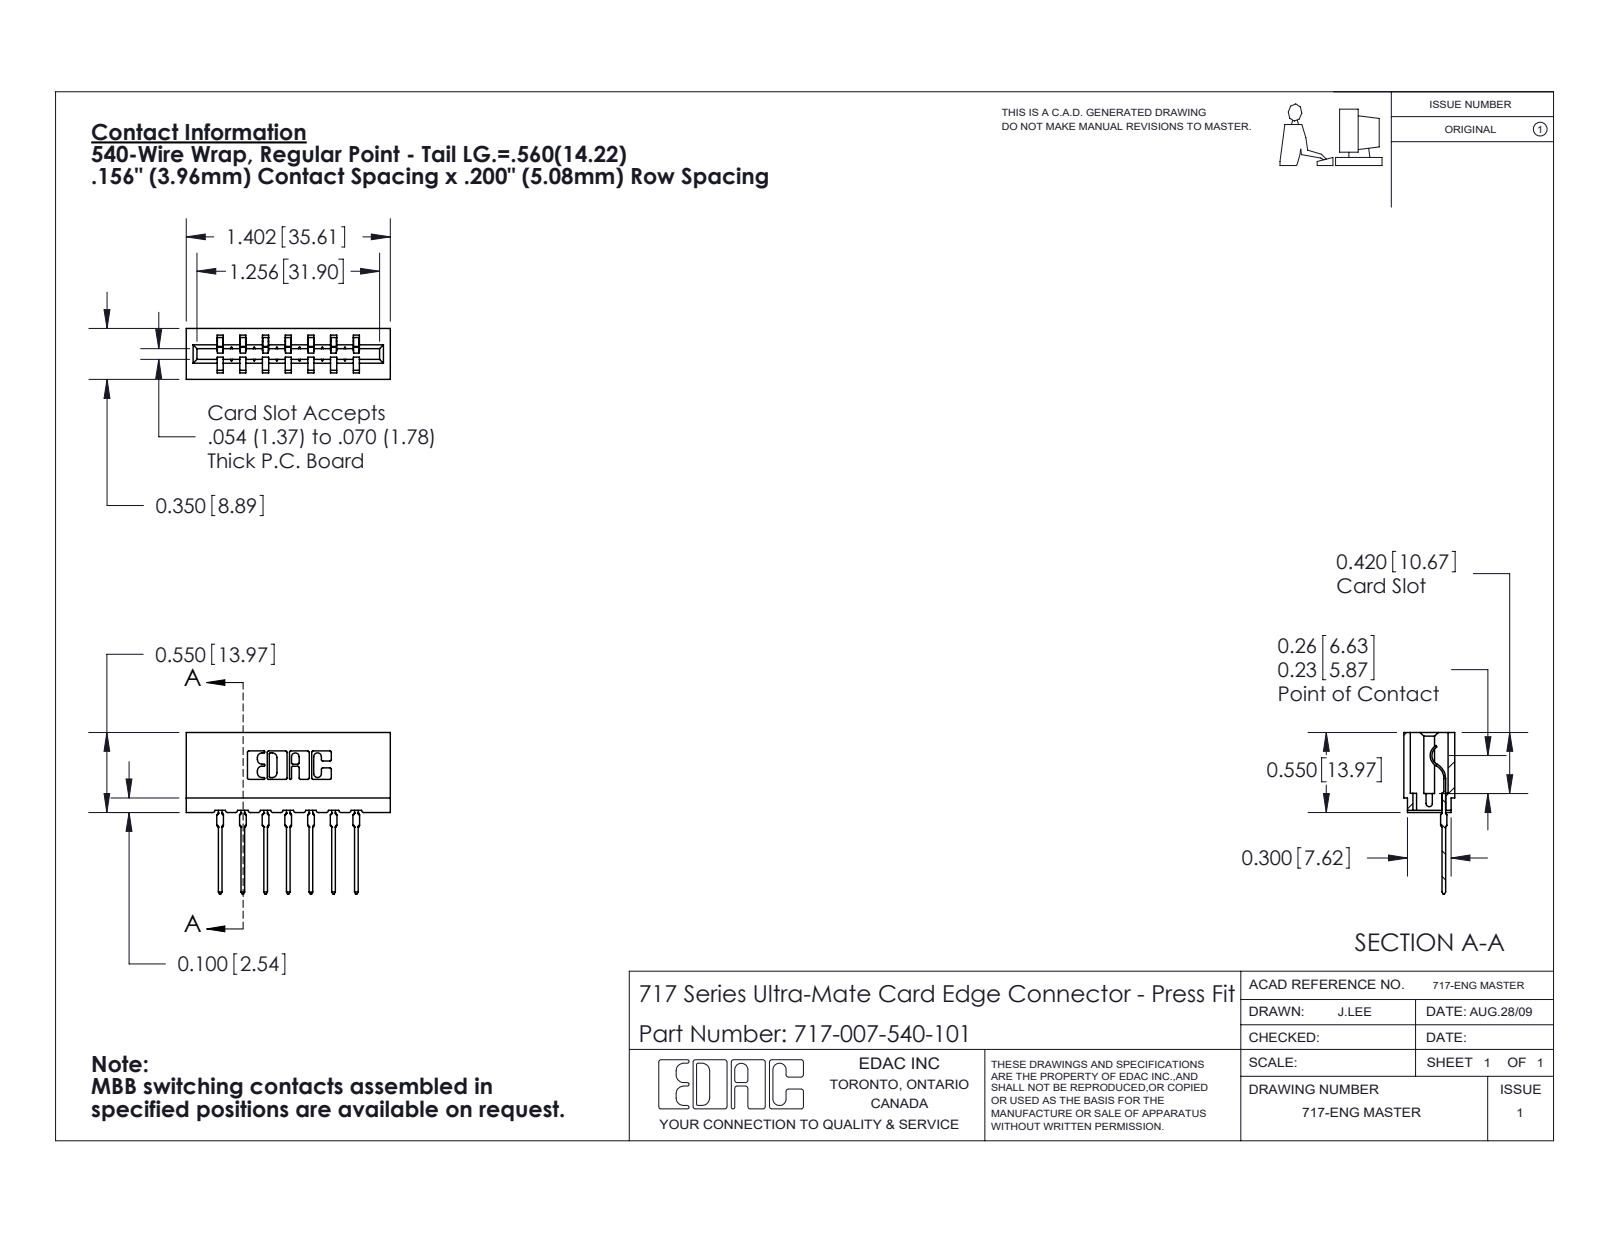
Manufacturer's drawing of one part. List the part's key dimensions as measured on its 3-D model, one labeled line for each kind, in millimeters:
Part name (STEP PRODUCT): 745-292-001_540; 717-007-540-101; 717 Part_Insulator Option - 06
STEP written by: SolidWorks 2020 (CONFIG_CONTROL_DESIGN)
Units: millimetres
Bodies: 8 solids, 885 faces (530 planar, 173 cylindrical, 182 other)
Overall size (bounding box): 35.6 × 28.2 × 8.9
Volume: 3 180 mm³ · Surface area: 4 170 mm²
Partial cylindrical surfaces — rounded edges, fillets, slot ends (radius × count): R0.3 ×22, R0.4 ×14, R0.5 ×14, R0.2 ×6, R0.8 ×6, R0.1 ×4, R0.3 ×4, R0.7 ×3
Main face-to-face distances: 5.4, 4, 3.5, 8.9, 11.9, 5, 7.9, 15.8, 1.1, 6.9
